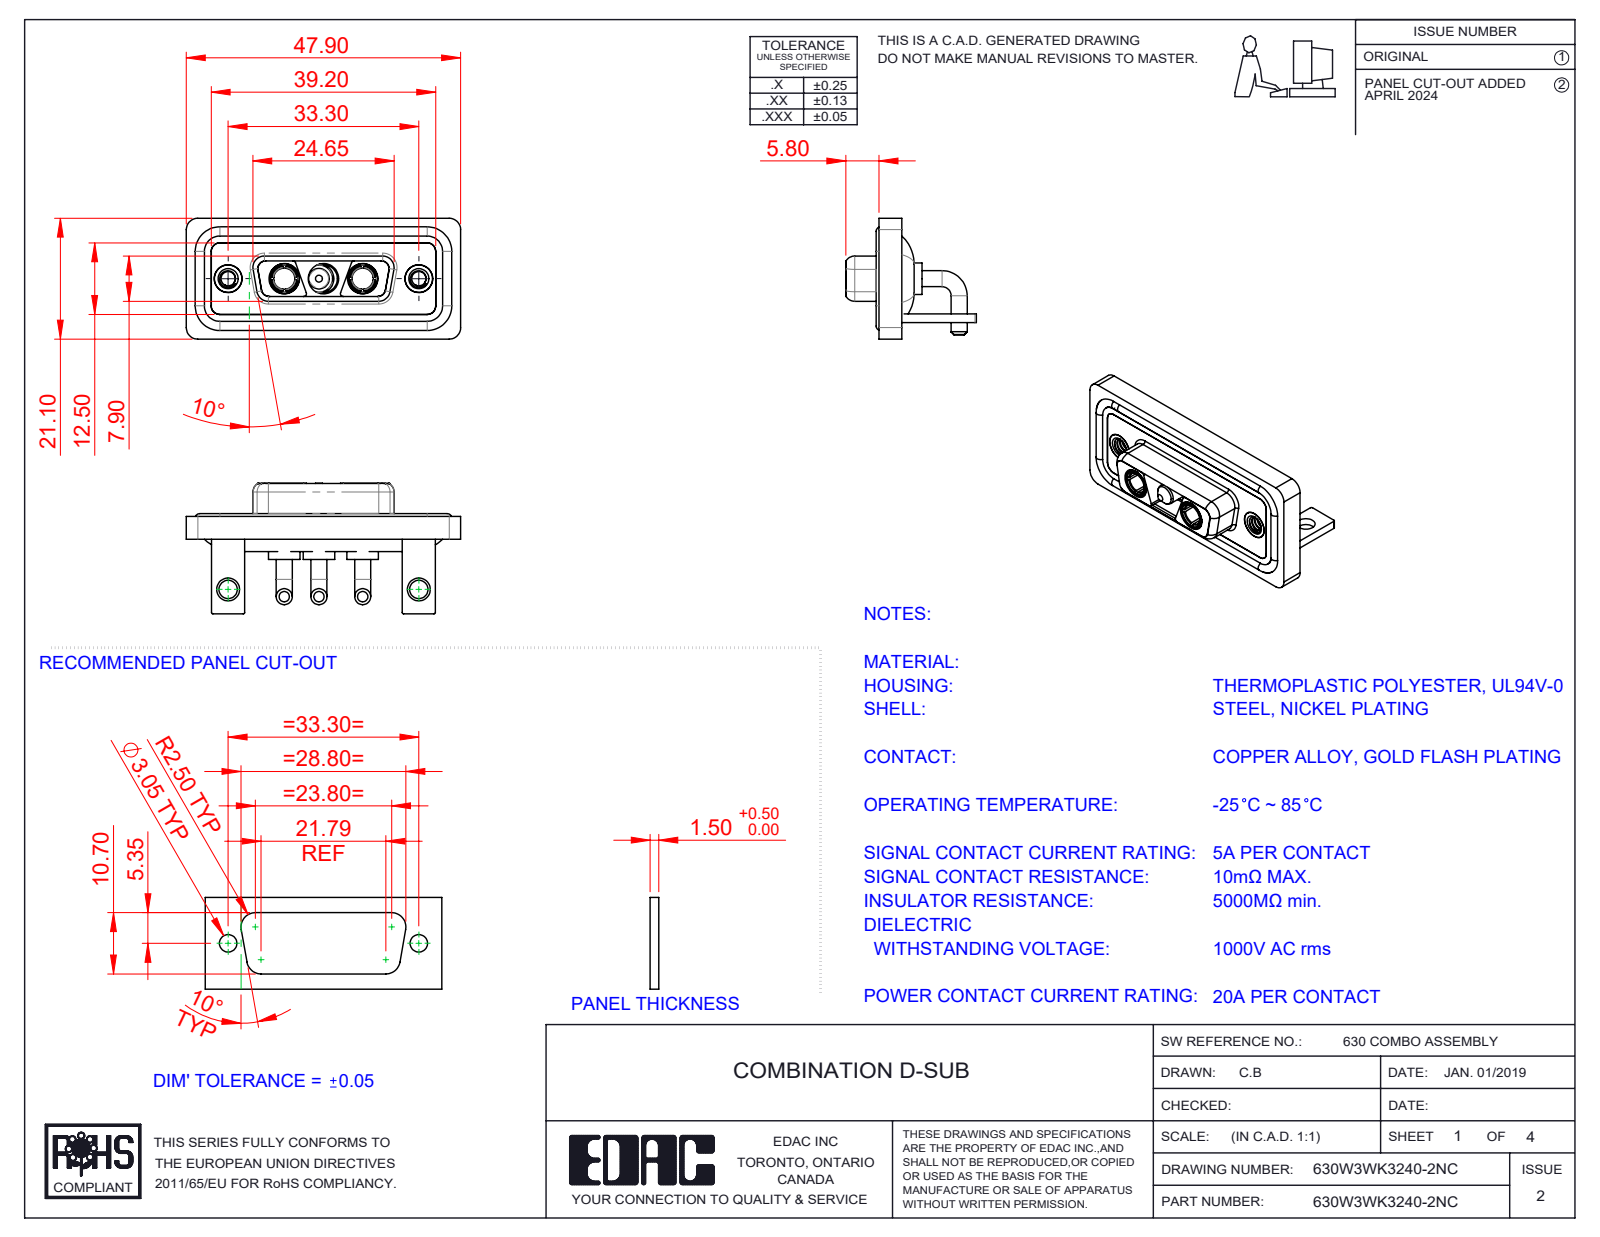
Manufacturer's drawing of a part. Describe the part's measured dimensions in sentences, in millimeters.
The part is named "630Combo Waterproof Housing_15 Contacts; Power Pin_20A RA; 630W3WK3140-2NC; 630Combo Shell Front_15 Contacts (+5 more)". Its 3-D file was written by "SolidWorks 2023 (CONFIG_CONTROL_DESIGN)". It is 15 solids with 637 faces: 198 planar, 286 cylindrical and 153 other. Overall it measures 47.9 by 22.8 by 21.1 millimeters. Its volume is 6 391 cubic millimeters and its surface area 10 477 square millimeters. Round holes: 5 of diameter 4.85, 3 of diameter 5.3, 2 of diameter 2.5, 2 of diameter 3.2, 2 of diameter 3.7, 2 of diameter 4, 2 of diameter 4.05, 2 of diameter 5. Round bosses or shafts: 6 of diameter 2.8, 4 of diameter 1.6, 3 of diameter 5.5, 3 of diameter 5.2, 3 of diameter 4.75, 3 of diameter 3.75, 2 of diameter 4.96, 2 of diameter 4.95. Partial cylindrical surfaces (rounded edges, fillets, slot ends): 21 of radius 2, 18 of radius 1.5, 16 of radius 0.25, 12 of radius 1.35, 9 of radius 0.5, 8 of radius 1.6, 4 of radius 0.6, 4 of radius 0.65. The main face-to-face distances are 0.4, 2.9, 1.5, 3.7, 1.8, 1.1, 4.1, 1.6, 2.5, 1.4. The hole center spacings are 6.85, 9.8, 16.65, 23.5, 33.3, 13.7.
